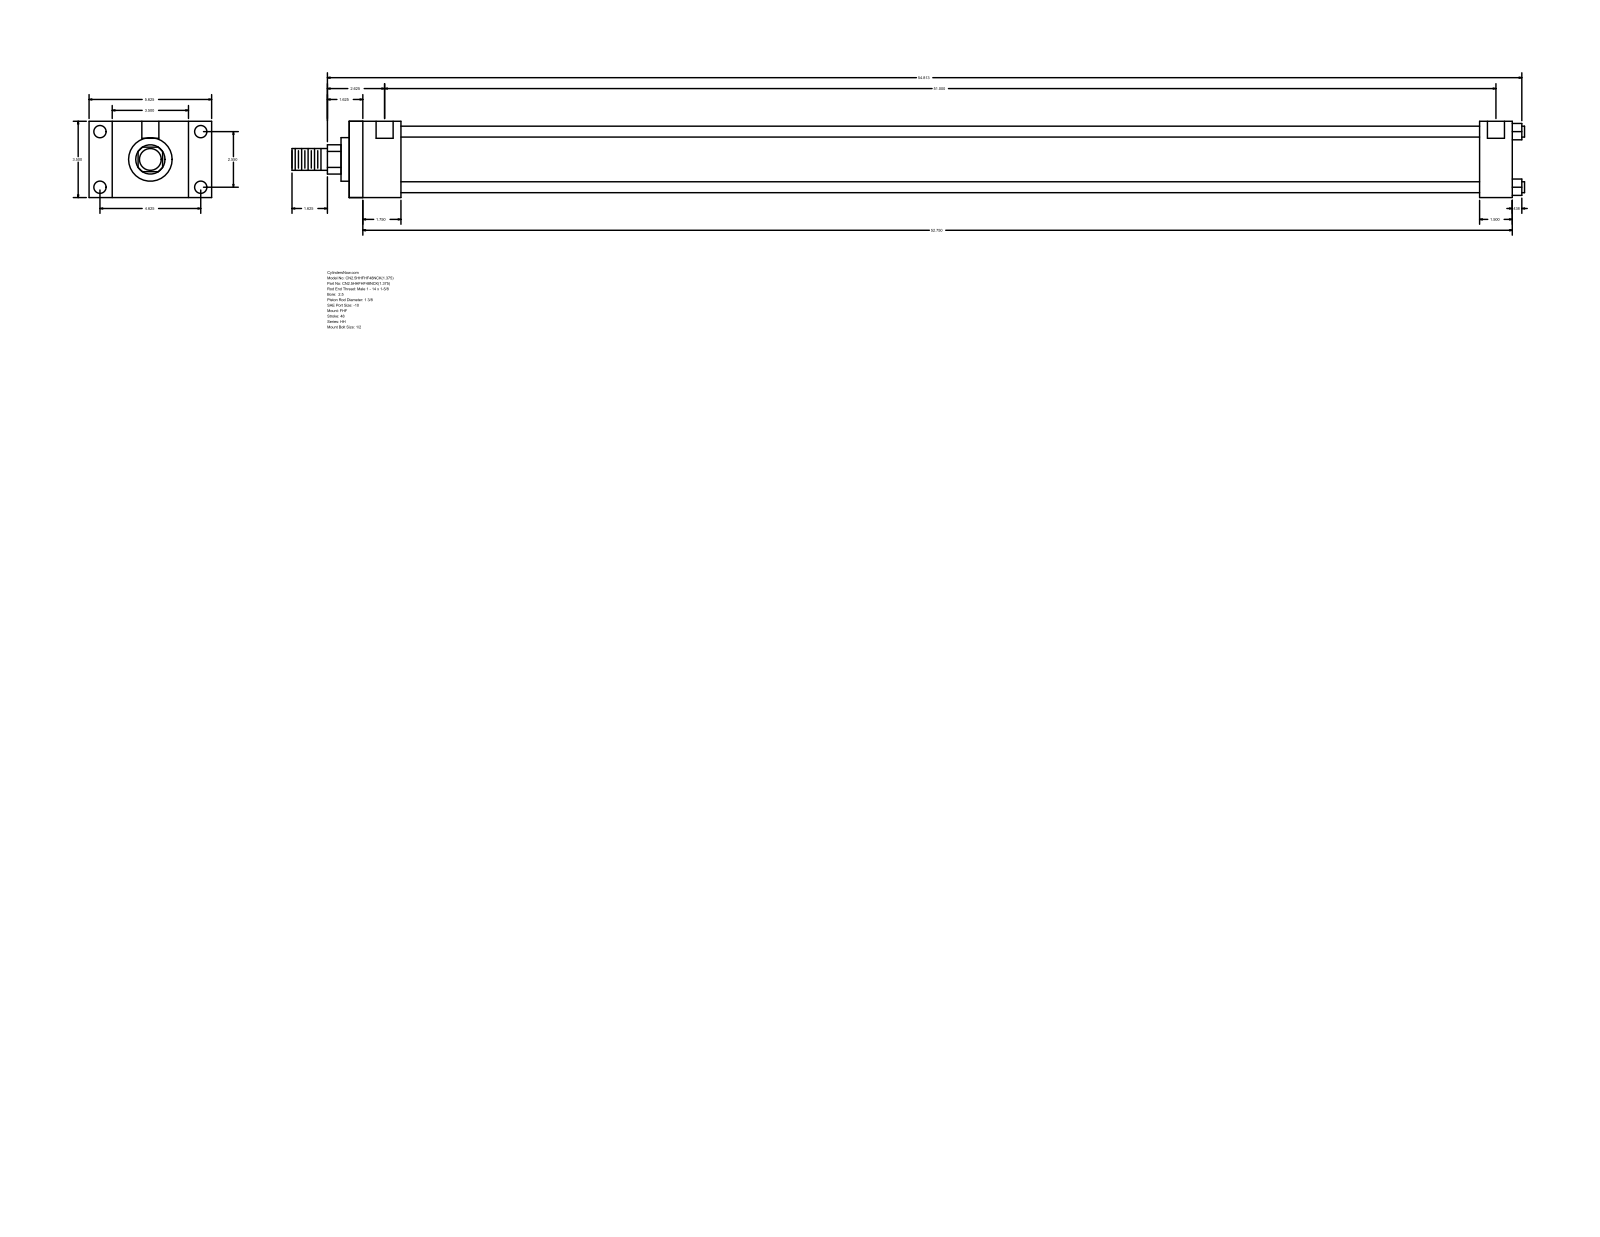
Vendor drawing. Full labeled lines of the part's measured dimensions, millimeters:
Part name (STEP PRODUCT): HH_FHF__0250_1.375
STEP written by: GSSL Pune (CONFIG_CONTROL_DESIGN)
Units: millimetres
Bodies: 0 solids, 88 faces (60 planar, 28 cylindrical, 0 other)
Overall size (bounding box): 1436.69 × 142.88 × 88.9
Round holes (diameter × count): ⌀5.56 ×4, ⌀14.3 ×4, ⌀19.84 ×2
Round bosses / shafts (diameter × count): ⌀12.7 ×4, ⌀73.03 ×1, ⌀50.8 ×1, ⌀34.92 ×1, ⌀25.4 ×1
Partial cylindrical surfaces — rounded edges, fillets, slot ends (radius × count): R17.06 ×1
Main face-to-face distances: 88.9, 60.32, 26.99, 115.89, 1355.72, 1295.4, 142.88, 1317.63, 1257.31, 38.09
Hole centre spacings: 1.58, 64.76, 117.48, 134.15, 1296.99, 1298.57, 1295.41
